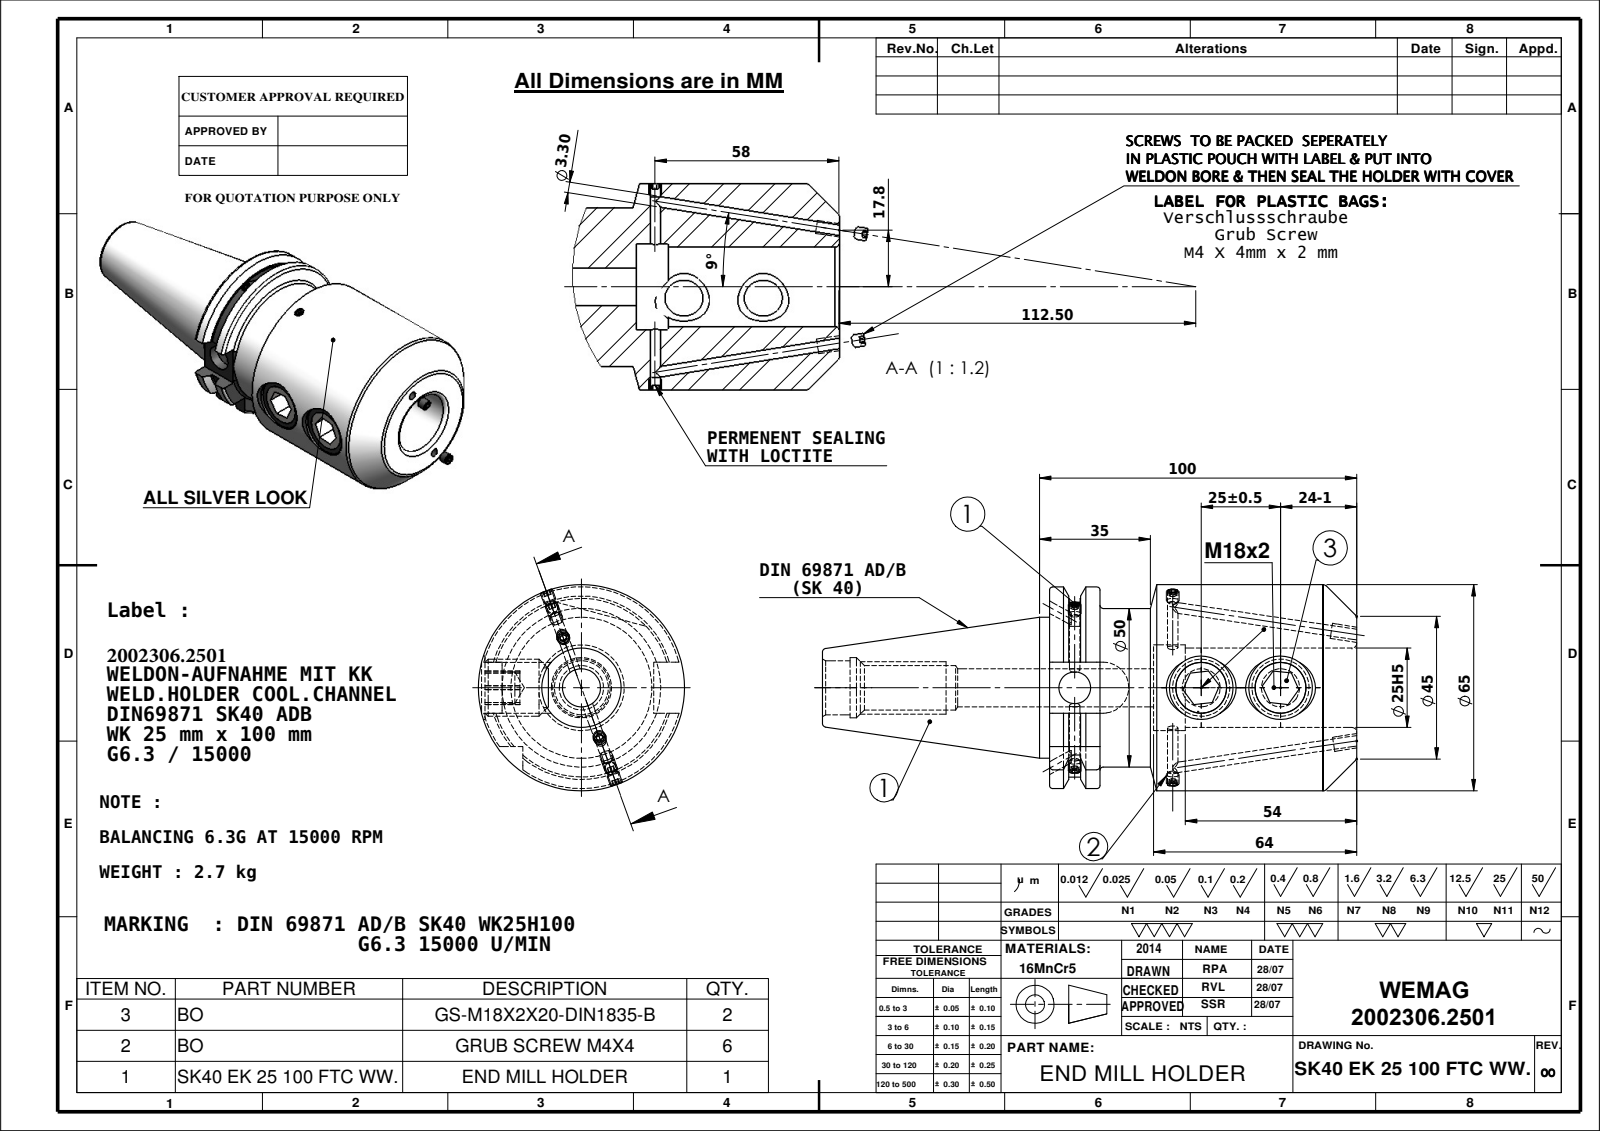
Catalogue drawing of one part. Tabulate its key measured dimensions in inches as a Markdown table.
| quantity | value |
| --- | --- |
| part name | SK40 EK 25 100 FTC WW.; Copy of M4X4_DIN 913 - M4 x 4-N; M4X4_DIN 913 - M4 x 4-N; GS-M18X2X20 |
| STEP written by | SolidWorks 2009 (CONFIG_CONTROL_DESIGN) |
| units | inches |
| bodies | 9 solids, 255 faces (103 planar, 69 cylindrical, 83 other) |
| overall size | 6.982 × 2.559 × 2.559 |
| volume | 18.31 in³ |
| surface area | 78.38 in² |
| round holes (diameter × count) | 0.13 × 5, 0.63 × 2, 0.787 × 2, 0.394 × 1, 0.472 × 1, 0.551 × 1, 0.669 × 1, 0.748 × 1, 0.984 × 1, 1.063 × 1 |
| round bosses / shafts (diameter × count) | 0.157 × 6, 0.709 × 2, 2.559 × 1, 1.969 × 1, 1.75 × 1 |
| partial cylindrical surfaces (radius × count) | 0.317 × 1, 1.107 × 1, 1.251 × 1 |
| main face-to-face distances | 3.811, 0.626, 3.185, 1.291, 0.665, 2.52, 2.094, 0.394, 0.787, 1.307 |
| hole center spacings | 1.217, 0.984, 1.569, 2.553 |
